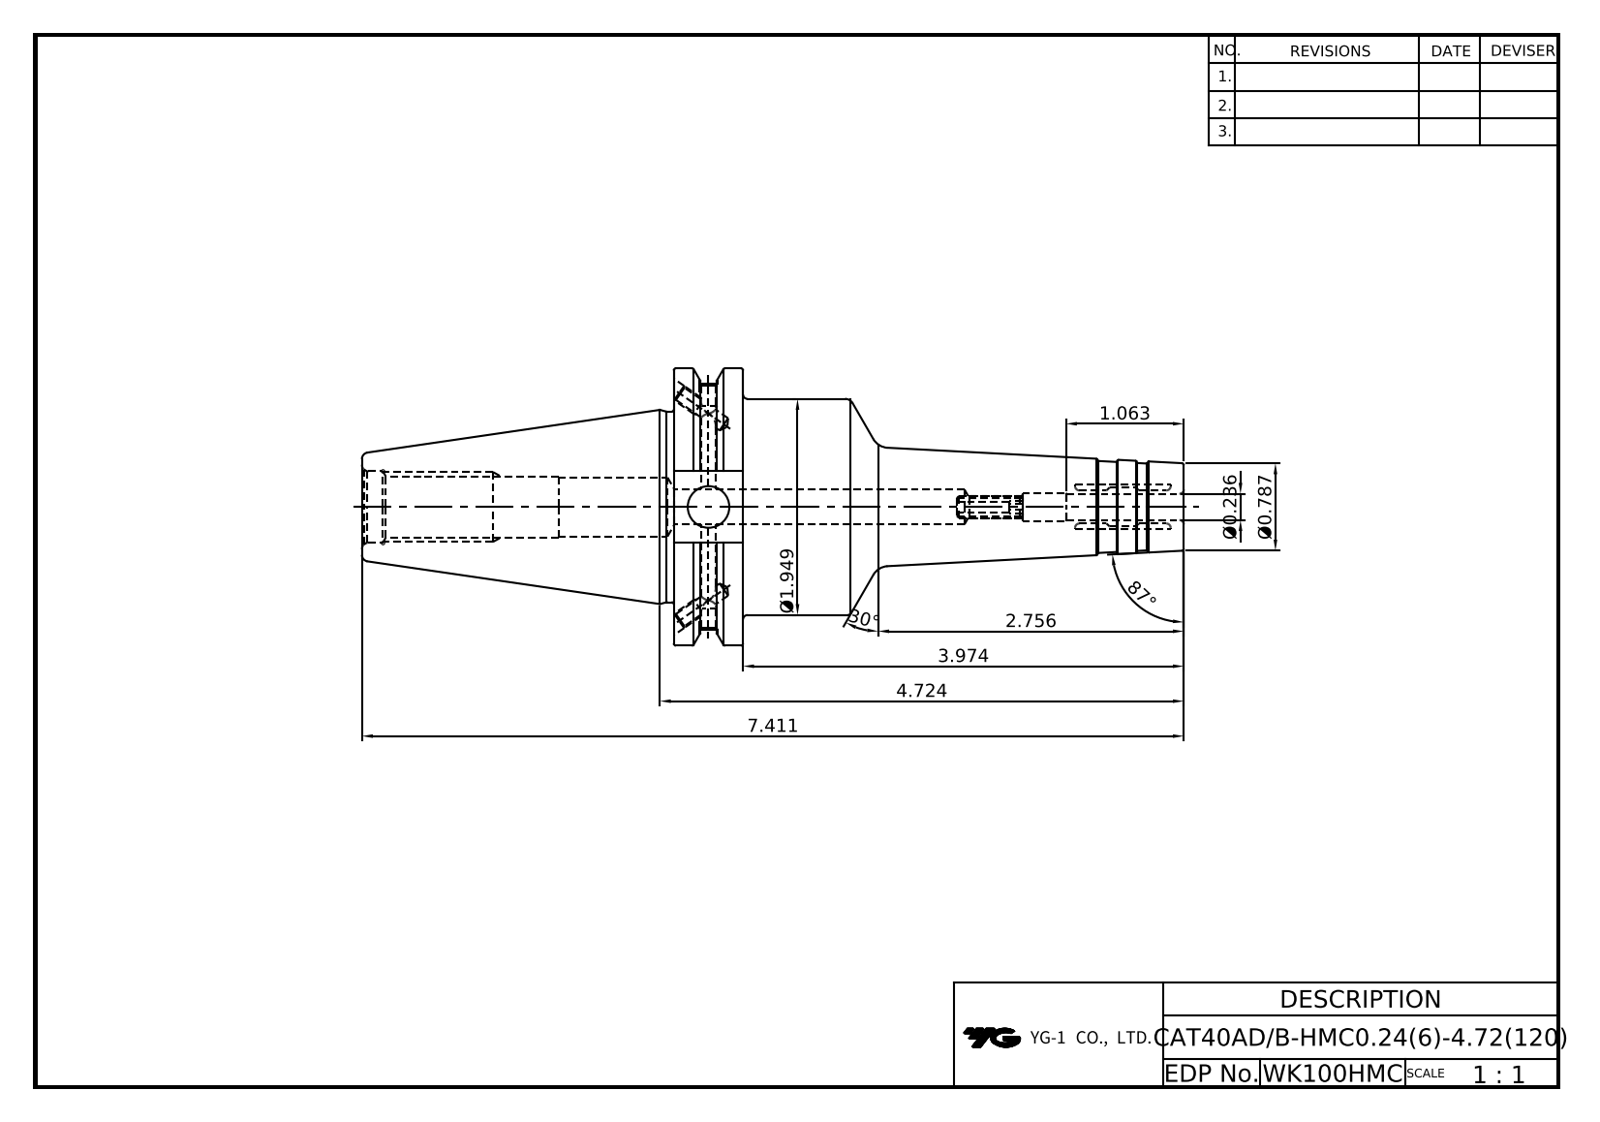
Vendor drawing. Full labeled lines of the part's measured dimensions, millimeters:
Part name (STEP PRODUCT): LO-CAT40ADB-HMC6-120
STEP written by: Autodesk Inventor 2020 (AUTOMOTIVE_DESIGN)
Units: millimetres
Bodies: 1 solid, 108 faces (36 planar, 31 cylindrical, 41 other)
Overall size (bounding box): 188.25 × 63.5 × 61.09
Volume: 183 749 mm³ · Surface area: 31 754 mm²
Round holes (diameter × count): ⌀3.24 ×4, ⌀4 ×2, ⌀4.2 ×2, ⌀4.92 ×1, ⌀6 ×1, ⌀6.6 ×1, ⌀8 ×1, ⌀9.53 ×1, ⌀13 ×1, ⌀13.39 ×1, ⌀16.3 ×1
Round bosses / shafts (diameter × count): ⌀63.5 ×1, ⌀49.5 ×1, ⌀43.6 ×1
Partial cylindrical surfaces — rounded edges, fillets, slot ends (radius × count): R8.19 ×1, R28.15 ×1
Main face-to-face distances: 15.88, 116.83, 100.95, 47.6, 16.38, 71.42, 87.3, 188.25, 77.47, 6.05
